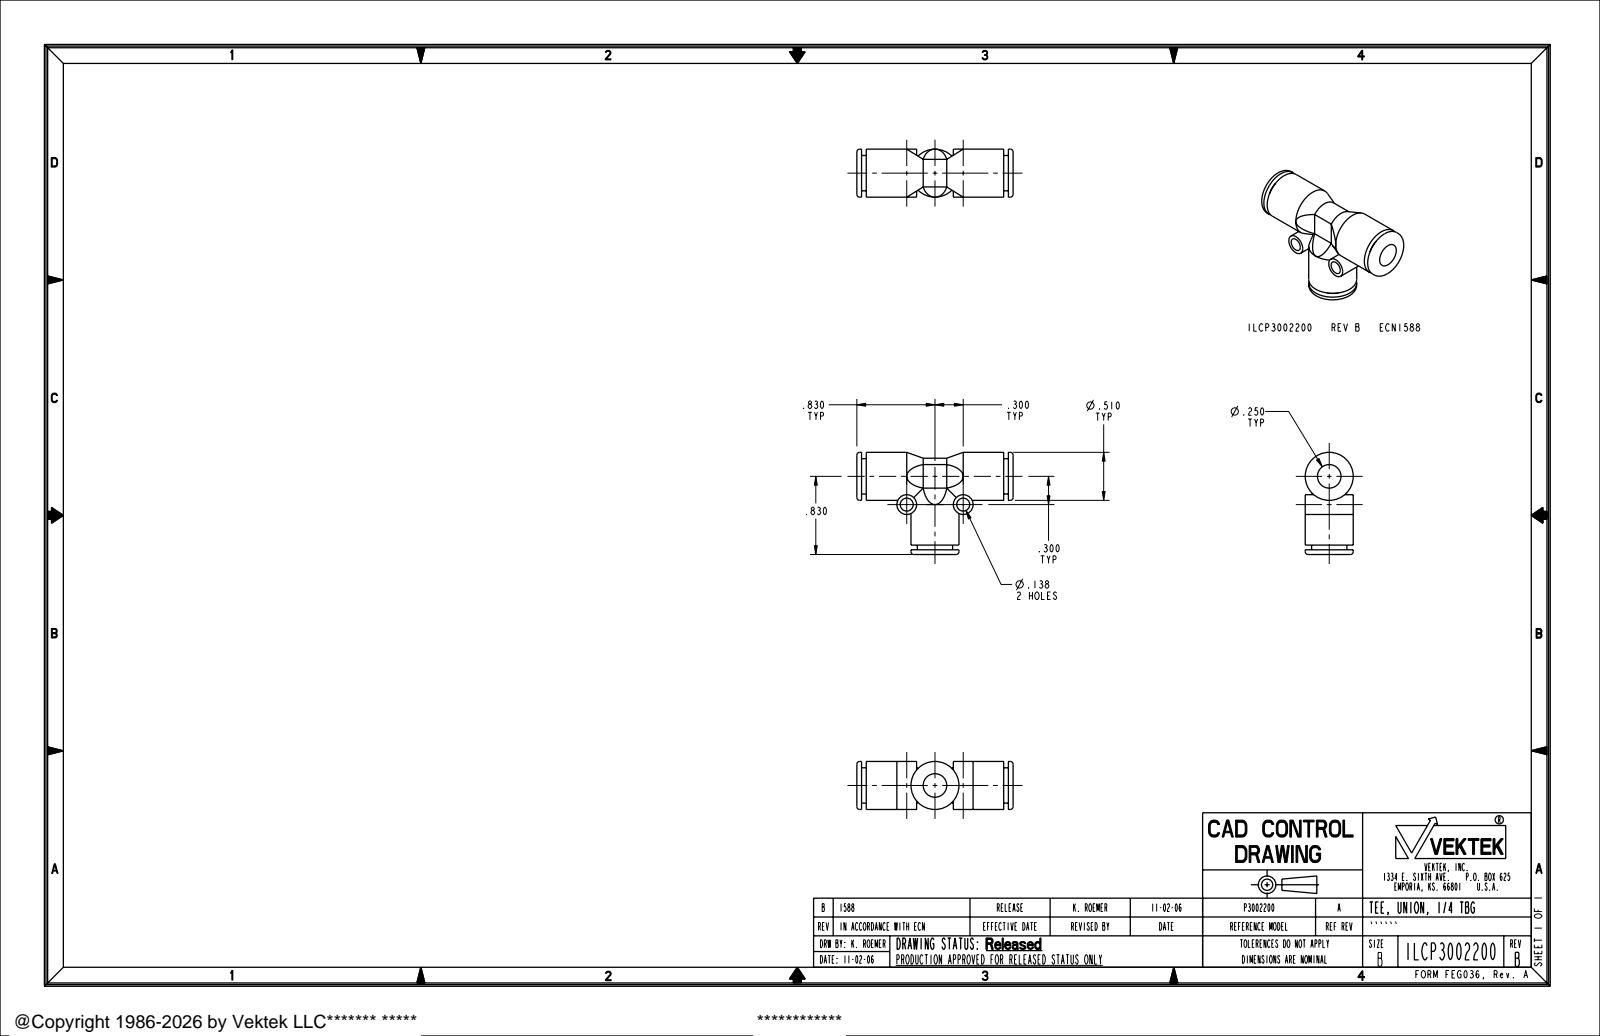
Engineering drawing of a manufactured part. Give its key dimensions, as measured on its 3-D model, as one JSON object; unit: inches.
{"part_name": "ILCP3002200", "step_written_by": "PRO/ENGINEER BY PARAMETRIC TECHNOLOGY CORPORATION, 2005180 (AUTOMOTIVE_DESIGN_CC2)", "units": "inches", "bodies": {"solids": 1, "faces": 68, "planar": 21, "cylindrical": 31, "other": 16}, "overall_size": [1.66, 1.085, 0.51], "volume_in3": 0.306, "surface_area_in2": 6.981, "round_holes": [[0.138, 2], [0.25, 2]], "round_bosses_or_shafts": [[0.51, 2], [0.375, 2], [0.21, 2]], "partial_cylinders_radius": [[0.192, 1]], "face_to_face_distances": [0.05, 0.1, 1.56, 1.61, 1.51, 1.66, 1.46, 0.109, 0.402, 0.117], "hole_center_spacings": [0.6]}
